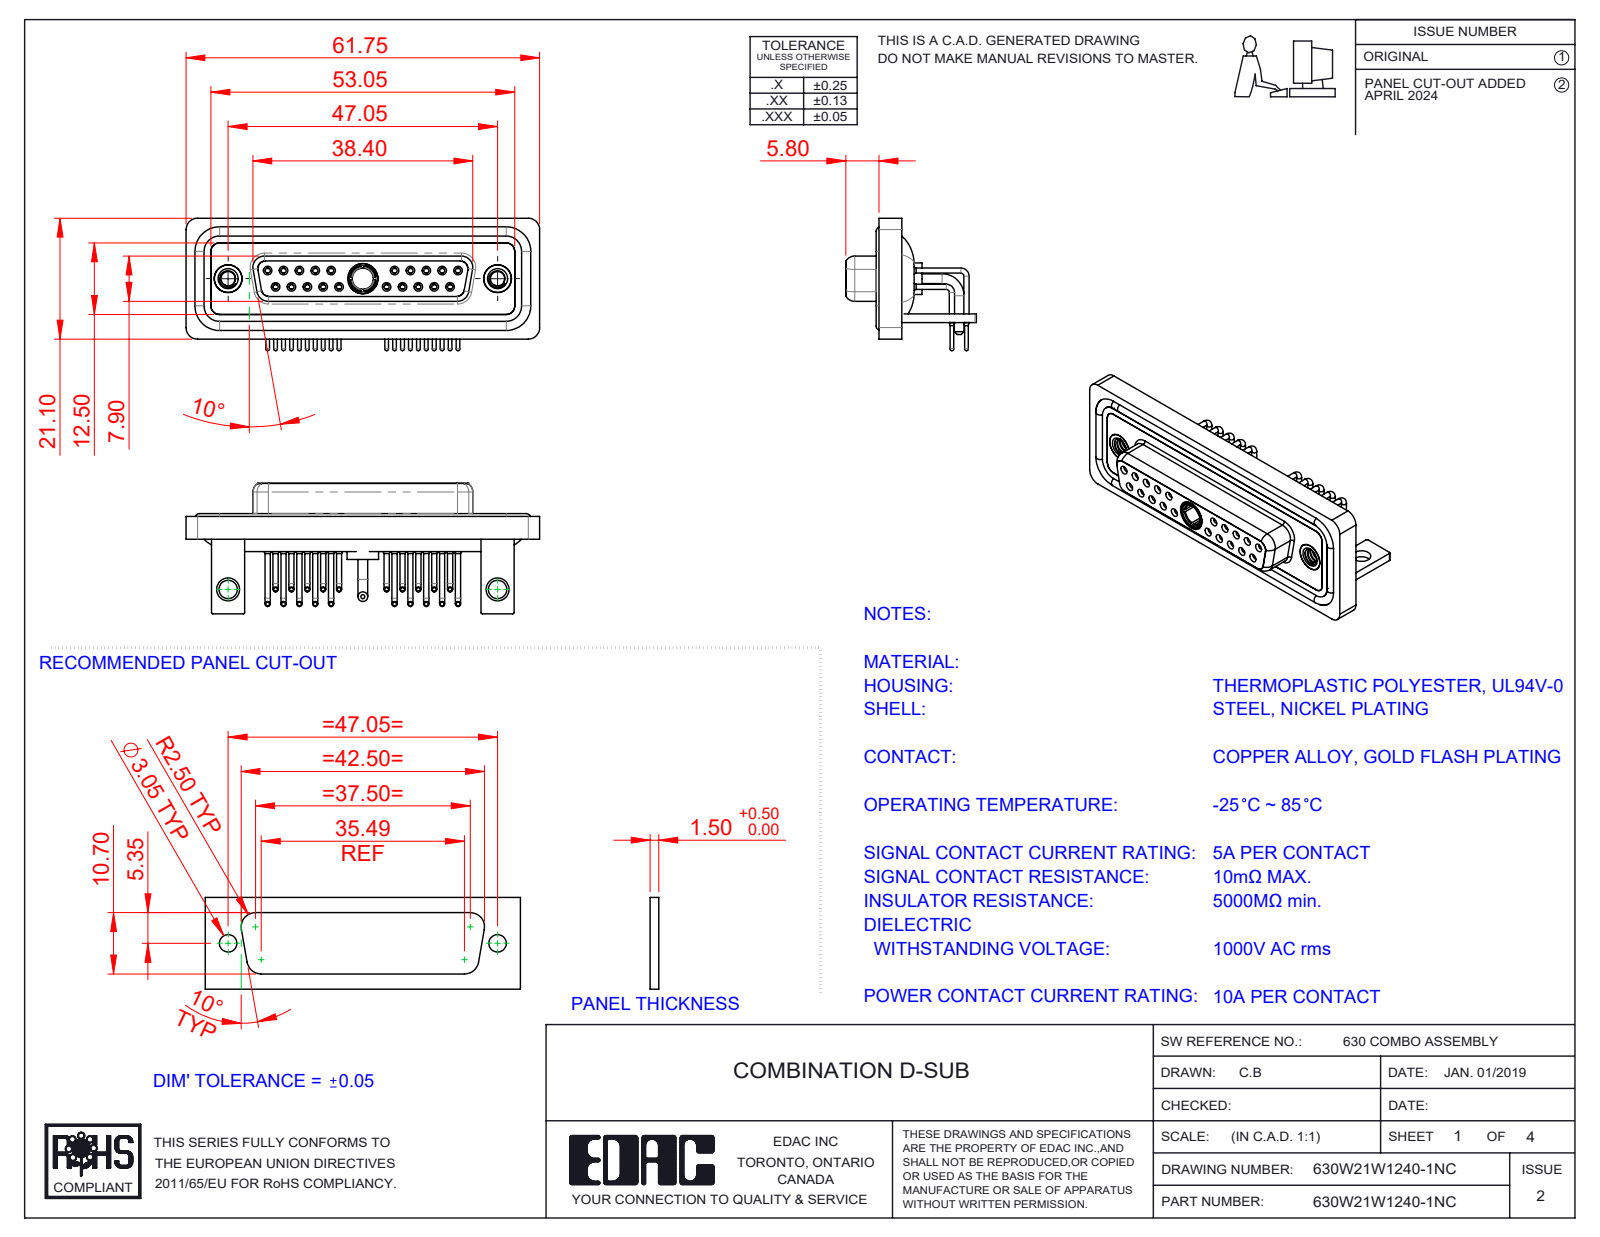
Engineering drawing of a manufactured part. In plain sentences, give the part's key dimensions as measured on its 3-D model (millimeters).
The part is named "Power Socket_10A RA; 630Combo Shell Rear_25 Contacts; 630Combo Stabilizer Bracket_50 Contacts; 630Combo Contact Row 1_50 Contacts (+6 more)". Its 3-D file was written by "SolidWorks 2023 (CONFIG_CONTROL_DESIGN)". It is 31 solids with 1566 faces: 454 planar, 695 cylindrical and 417 other. Overall it measures 61.75 by 23.12 by 22.8 millimeters. Its volume is 8 807 cubic millimeters and its surface area 15 468 square millimeters. Round holes: 20 of diameter 0.9, 20 of diameter 1.1, 20 of diameter 1.5, 20 of diameter 2, 10 of diameter 1.6, 10 of diameter 1.7, 3 of diameter 4.85, 2 of diameter 2.5, 2 of diameter 3.2, 2 of diameter 4, 2 of diameter 4.05, 2 of diameter 5. Round bosses or shafts: 20 of diameter 0.9, 20 of diameter 0.65, 14 of diameter 1.6, 2 of diameter 4.95, 2 of diameter 4.8, 2 of diameter 1.7, 1 of diameter 5.5, 1 of diameter 5.2. Partial cylindrical surfaces (rounded edges, fillets, slot ends): 19 of radius 2, 18 of radius 1.5, 16 of radius 0.25, 8 of radius 1.35, 8 of radius 1.6, 5 of radius 0.5, 4 of radius 0.6, 4 of radius 0.65. The main face-to-face distances are 0.4, 1.8, 2.9, 3.7, 1.5, 4.1, 1.1, 1.4, 1.6, 2.5. The hole center spacings are 3.16, 2.77, 5.54, 8.31, 5.04, 19.39, 20.97, 22.16.
